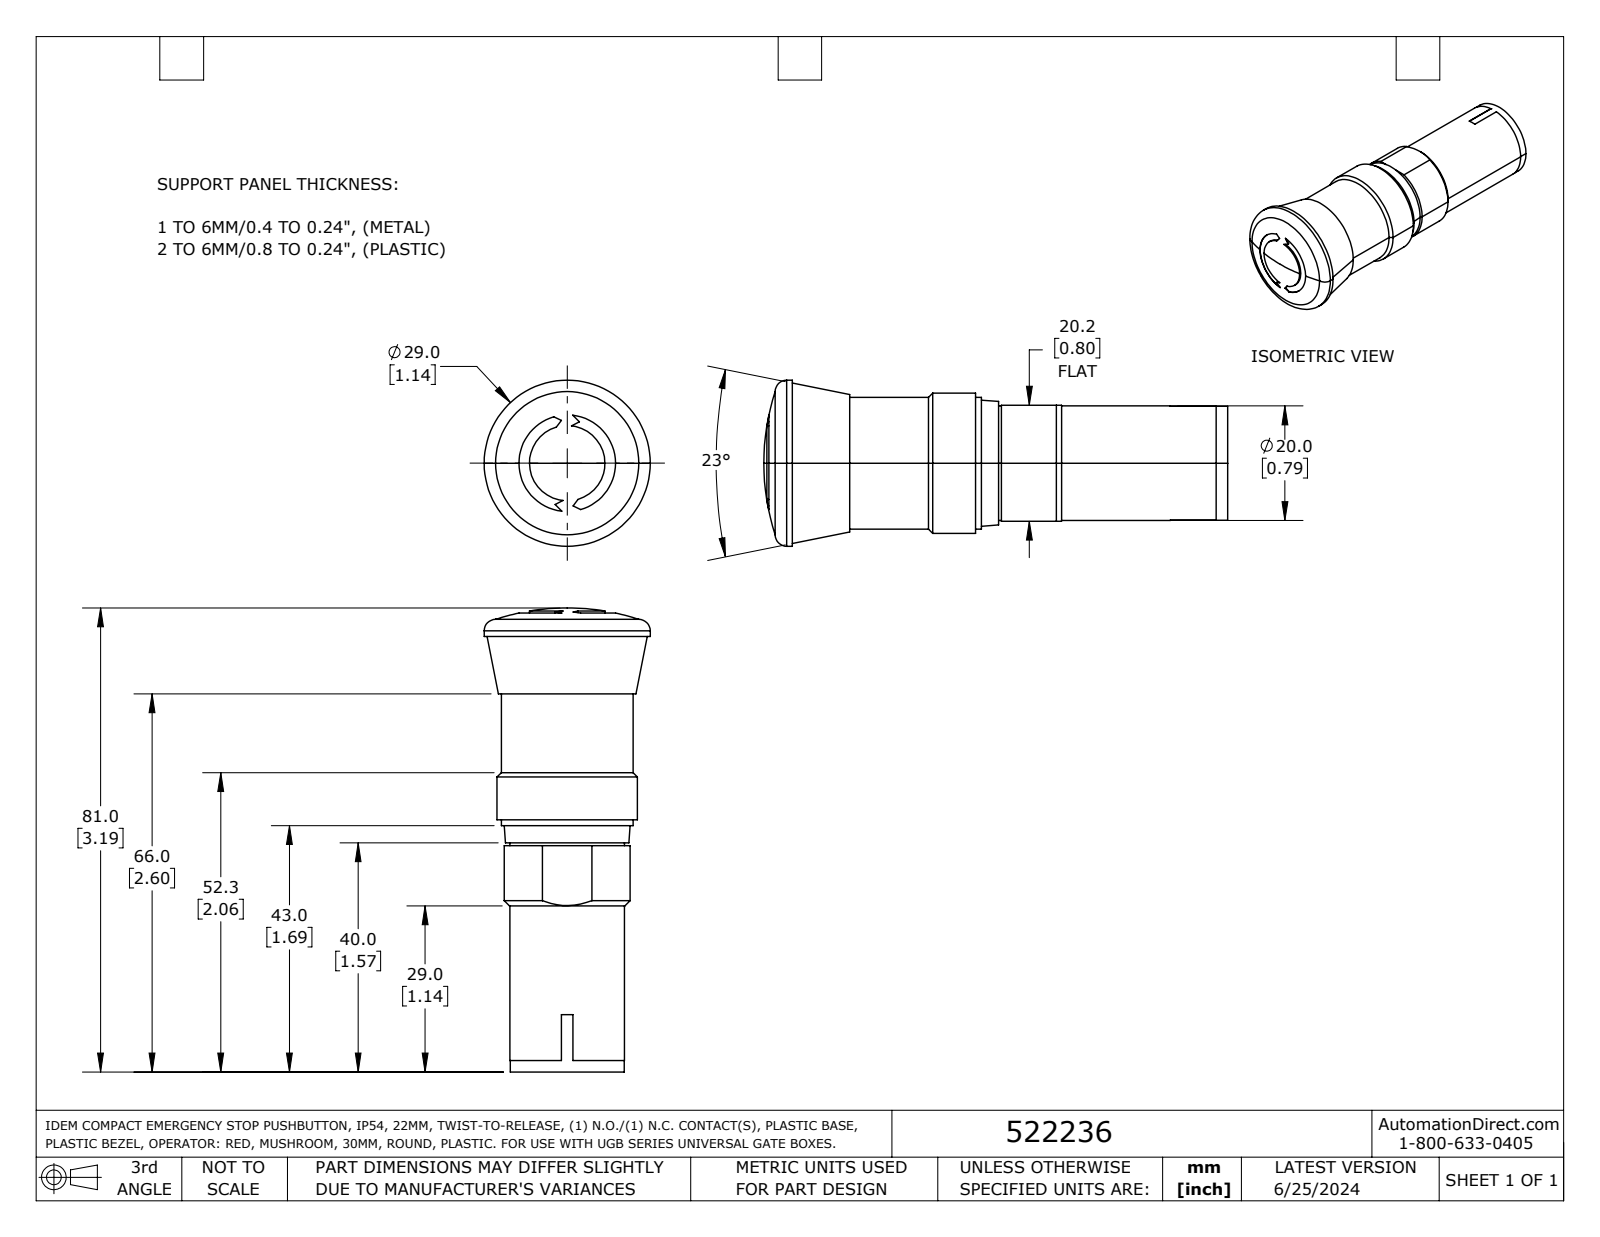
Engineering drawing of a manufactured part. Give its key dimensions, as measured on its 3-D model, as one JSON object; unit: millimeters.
{"part_name": "522236", "step_written_by": "SolidWorks 2023 (AUTOMOTIVE_DESIGN)", "units": "millimeters", "bodies": {"solids": 1, "faces": 62, "planar": 28, "cylindrical": 22, "other": 12}, "overall_size": [81, 29, 29], "volume_mm3": 31940, "surface_area_mm2": 6839, "round_holes": [[16.9, 1]], "round_bosses_or_shafts": [[29, 1], [24.5, 1], [23, 1], [20, 1], [19.9, 1]], "partial_cylinders_radius": [[6.6, 2], [11, 1]], "face_to_face_distances": [20.2, 80, 36, 44, 40.5, 4.5, 39.5, 40, 4, 0.5]}
